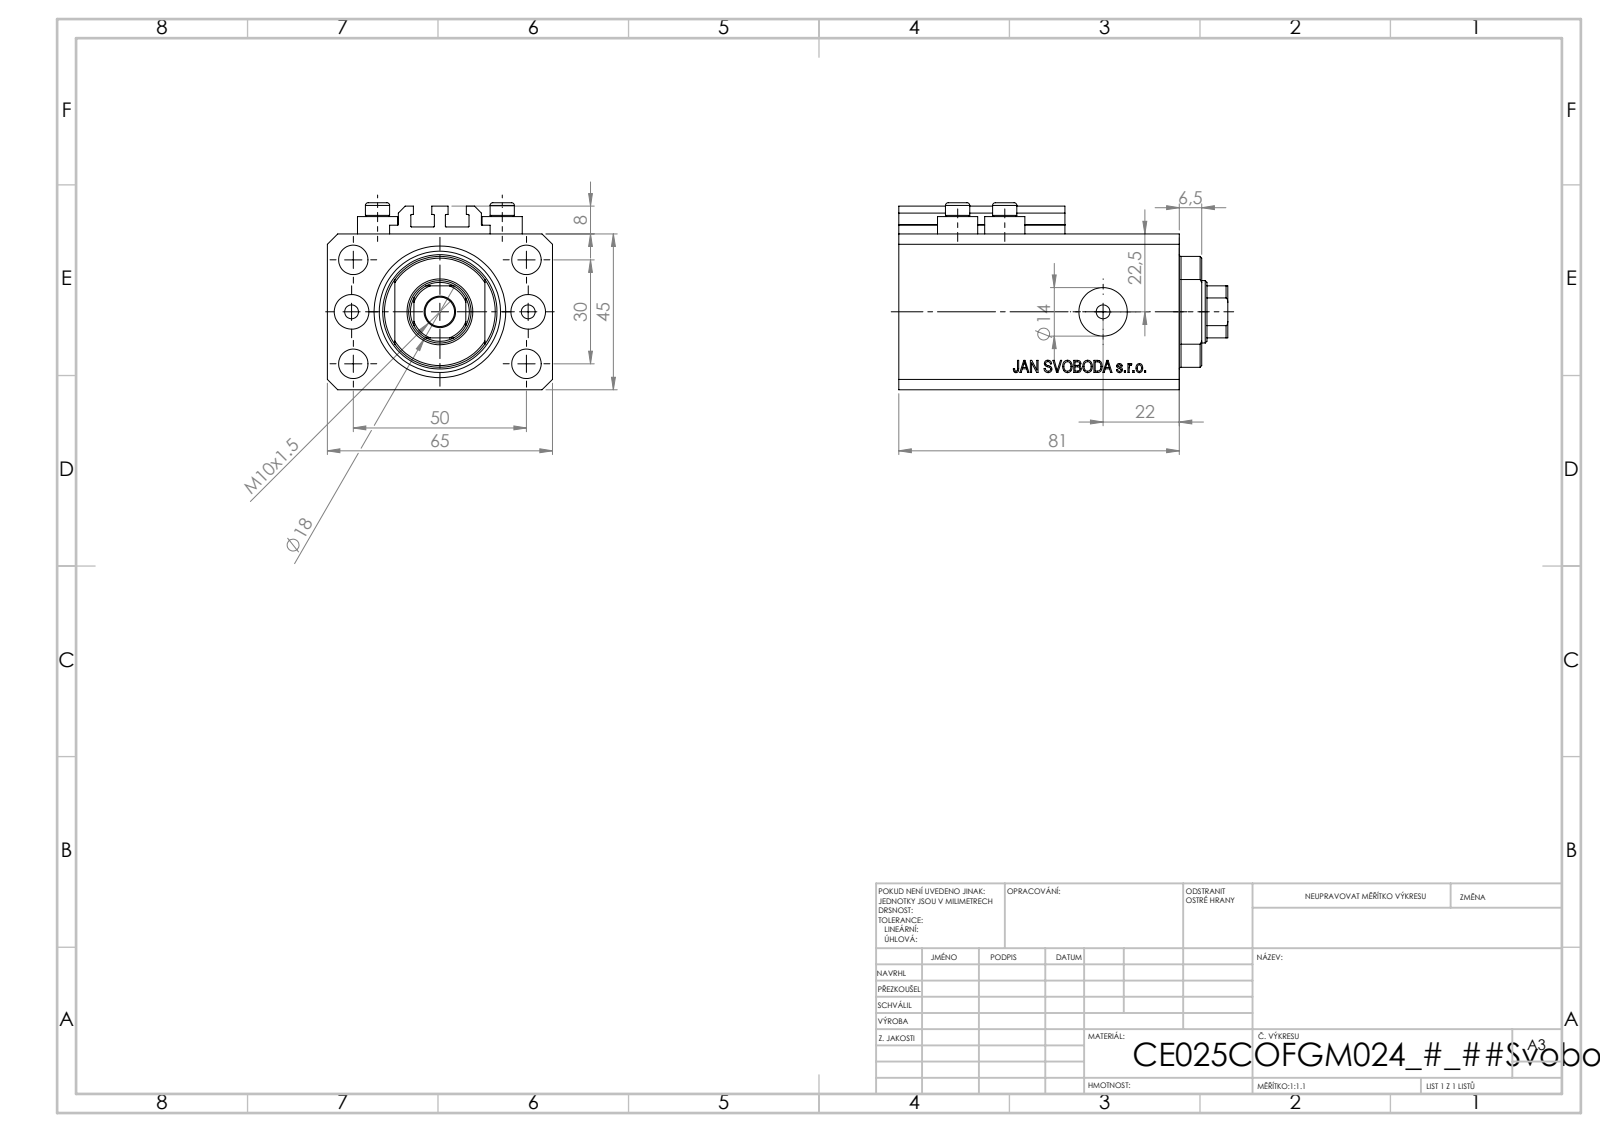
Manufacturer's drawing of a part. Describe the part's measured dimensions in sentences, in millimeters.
The part is named "V250CE_C_VCP; V250CE_VC_C; ALLEN BOLT V250CE; V250CE_C_Body". Its 3-D file was written by "SolidWorks 2019 (CONFIG_CONTROL_DESIGN)". It is 8 solids with 1034 faces: 504 planar, 86 cylindrical and 444 other. Overall it measures 95 by 65 by 54 millimeters. Its volume is 222 218 cubic millimeters and its surface area 59 488 square millimeters. Round holes: 8 of diameter 4, 5 of diameter 8.5, 2 of diameter 10, 2 of diameter 14, 1 of diameter 18, 1 of diameter 25, 1 of diameter 38. Round bosses or shafts: 4 of diameter 11.6, 4 of diameter 7. Partial cylindrical surfaces (rounded edges, fillets, slot ends): 10 of radius 0.2, 1 of radius 8.5, 1 of radius 16. The main face-to-face distances are 45, 65, 14, 67, 81, 6.9, 60.1, 74.1, 47, 3. The hole center spacings are 15.01, 29.15, 52.68, 13.6, 25.5, 30, 36, 38.48.
